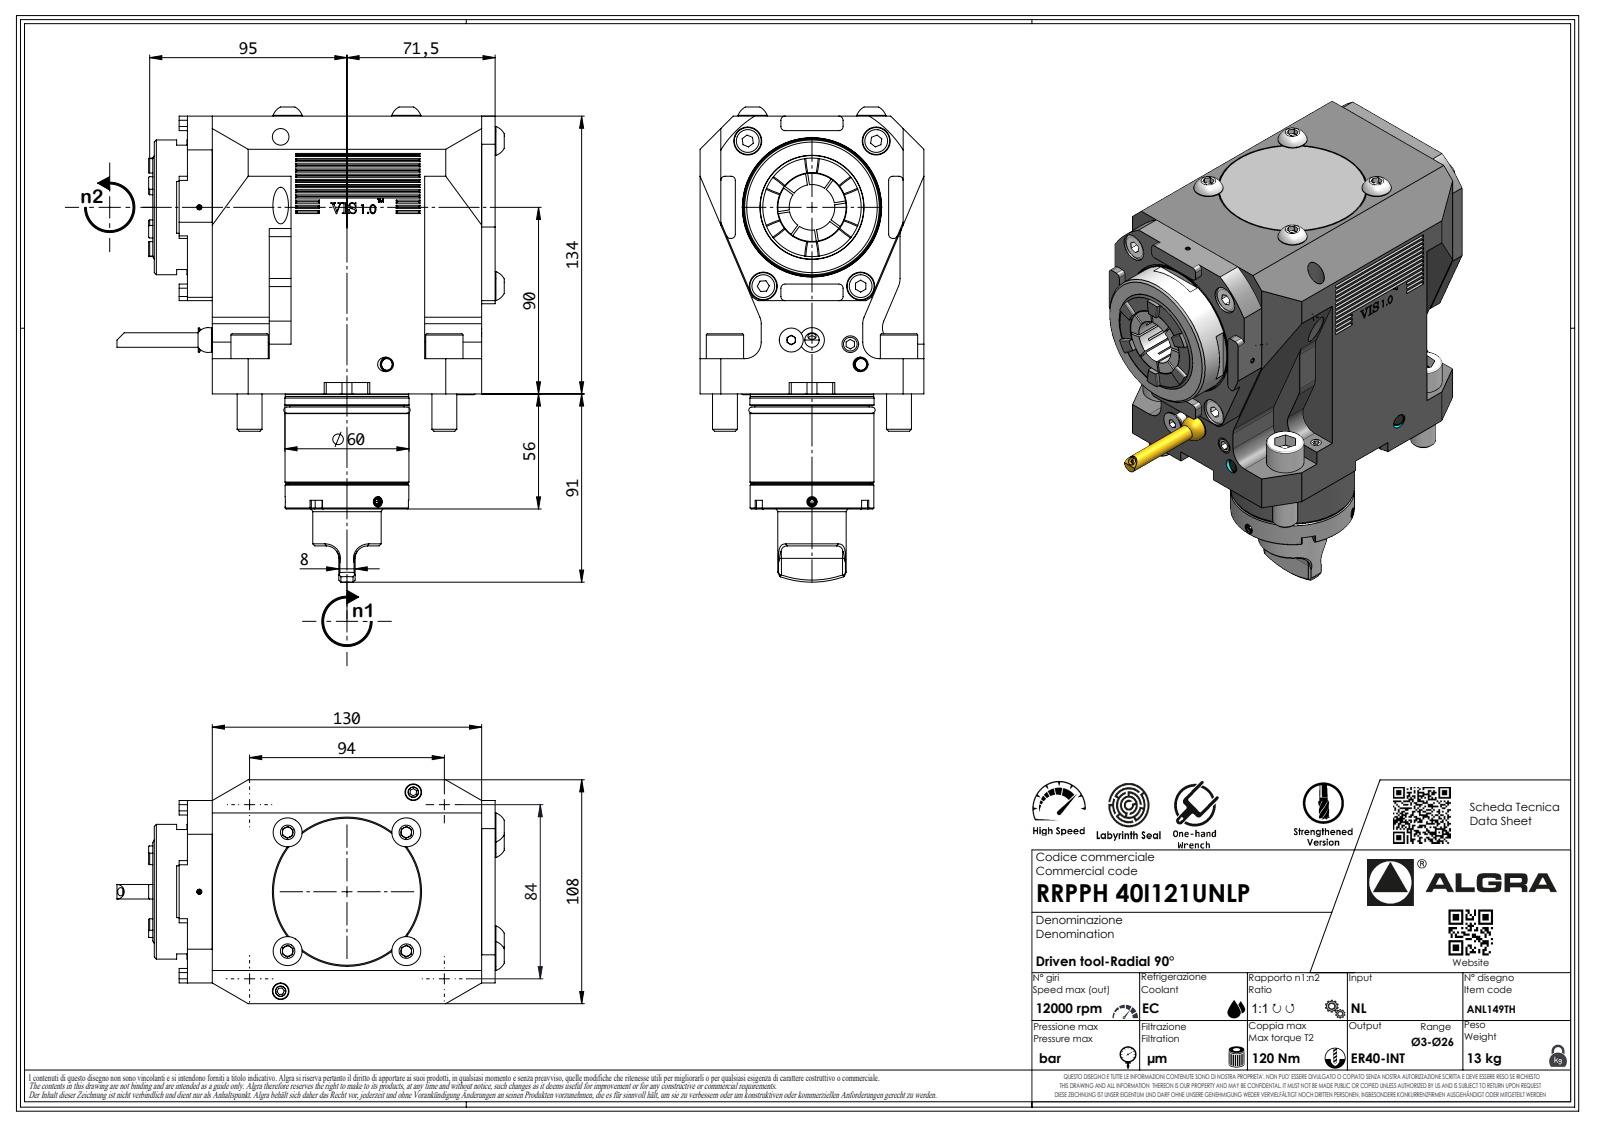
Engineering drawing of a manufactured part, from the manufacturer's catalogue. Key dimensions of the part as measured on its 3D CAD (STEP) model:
Part name (STEP PRODUCT): RRPPH40I121UNLP
STEP written by: SolidWorks 2023 (AUTOMOTIVE_DESIGN)
Units: millimetres
Bodies: 1 solid, 950 faces (653 planar, 127 cylindrical, 170 other)
Overall size (bounding box): 224.8 × 182.5 × 108
Volume: 2 032 000 mm³ · Surface area: 126 276 mm²
Round holes (diameter × count): ⌀2.1 ×1, ⌀4 ×1
Round bosses / shafts (diameter × count): ⌀18 ×4, ⌀12 ×4, ⌀65 ×1, ⌀59.9 ×1, ⌀59.8 ×1, ⌀59.7 ×1, ⌀59.5 ×1, ⌀55.2 ×1
Partial cylindrical surfaces — rounded edges, fillets, slot ends (radius × count): R0.2 ×21, R8 ×18, R2 ×16, R6 ×10, R0.33 ×7, R0.52 ×7, R3.7 ×7, R10 ×4
Main face-to-face distances: 108, 134, 12, 27.5, 16, 28, 102.5, 55.5, 6.5, 136.5
